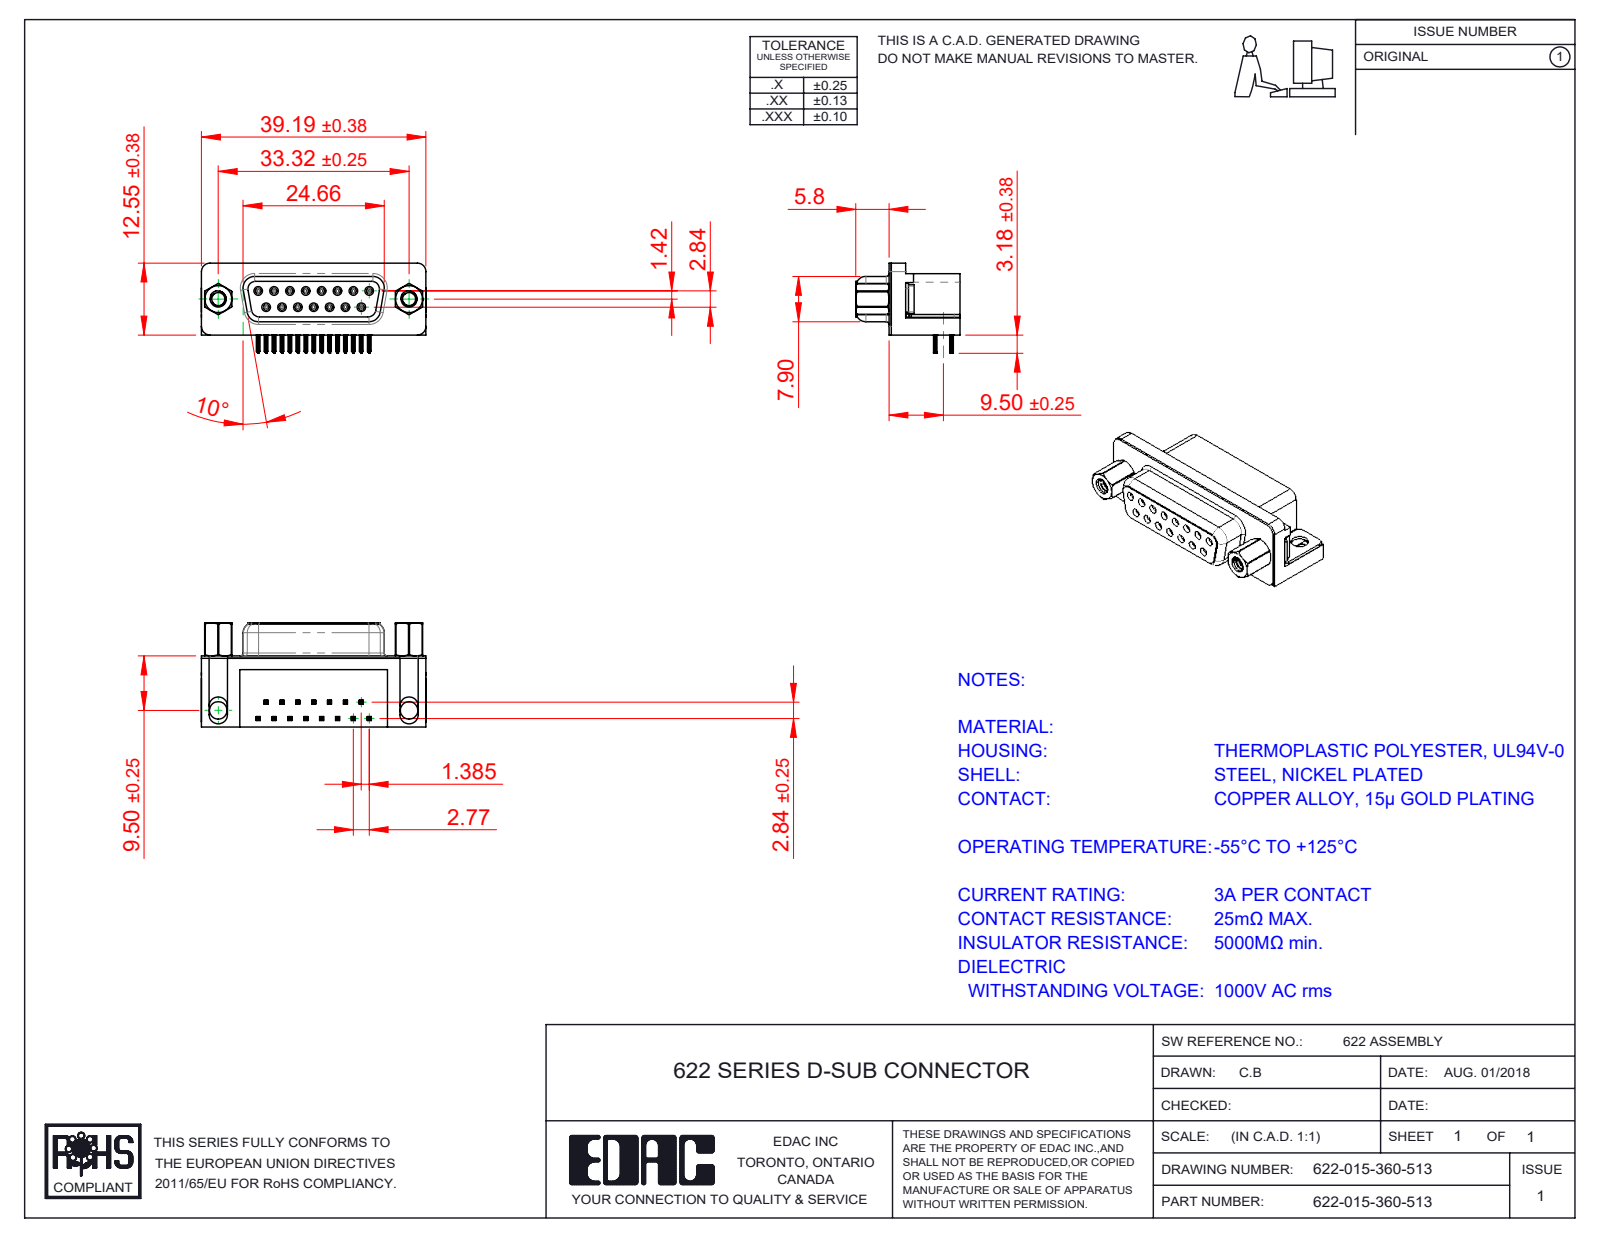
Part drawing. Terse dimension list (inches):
name: 622-015-360-513; 622 4-40 Threaded Rivet; 622 Shell_15 Socket; 622 Thru Hole Board Mount (+4 more)
written by: SolidWorks 2016 (CONFIG_CONTROL_DESIGN)
unit: in
bodies: 23 solids, 2545 faces (1094 planar, 669 cylindrical, 782 other)
size: 1.544 × 0.717 × 0.619
volume: 0.329 in³; area: 11.09 in²
holes: 15× ⌀0.031, 15× ⌀0.035, 2× ⌀0.089, 2× ⌀0.09, 2× ⌀0.12, 2× ⌀0.157, 2× ⌀0.189, 2× ⌀0.197
bosses: 15× ⌀0.047, 2× ⌀0.193, 2× ⌀0.187, 2× ⌀0.154, 2× ⌀0.11
rounds: 120× R0.004, 60× R0.006, 30× R0.014, 18× R0.039, 15× R0.013, 8× R0.01, 8× R0.053, 8× R0.059
face distances: 0.016, 0.472, 0.244, 0.488, 0.407, 0.114, 0.228, 0.262, 0.033, 0.014
hole spacings: 0.124, 0.109, 0.218, 0.327, 0.436, 0.198, 0.198, 0.294
